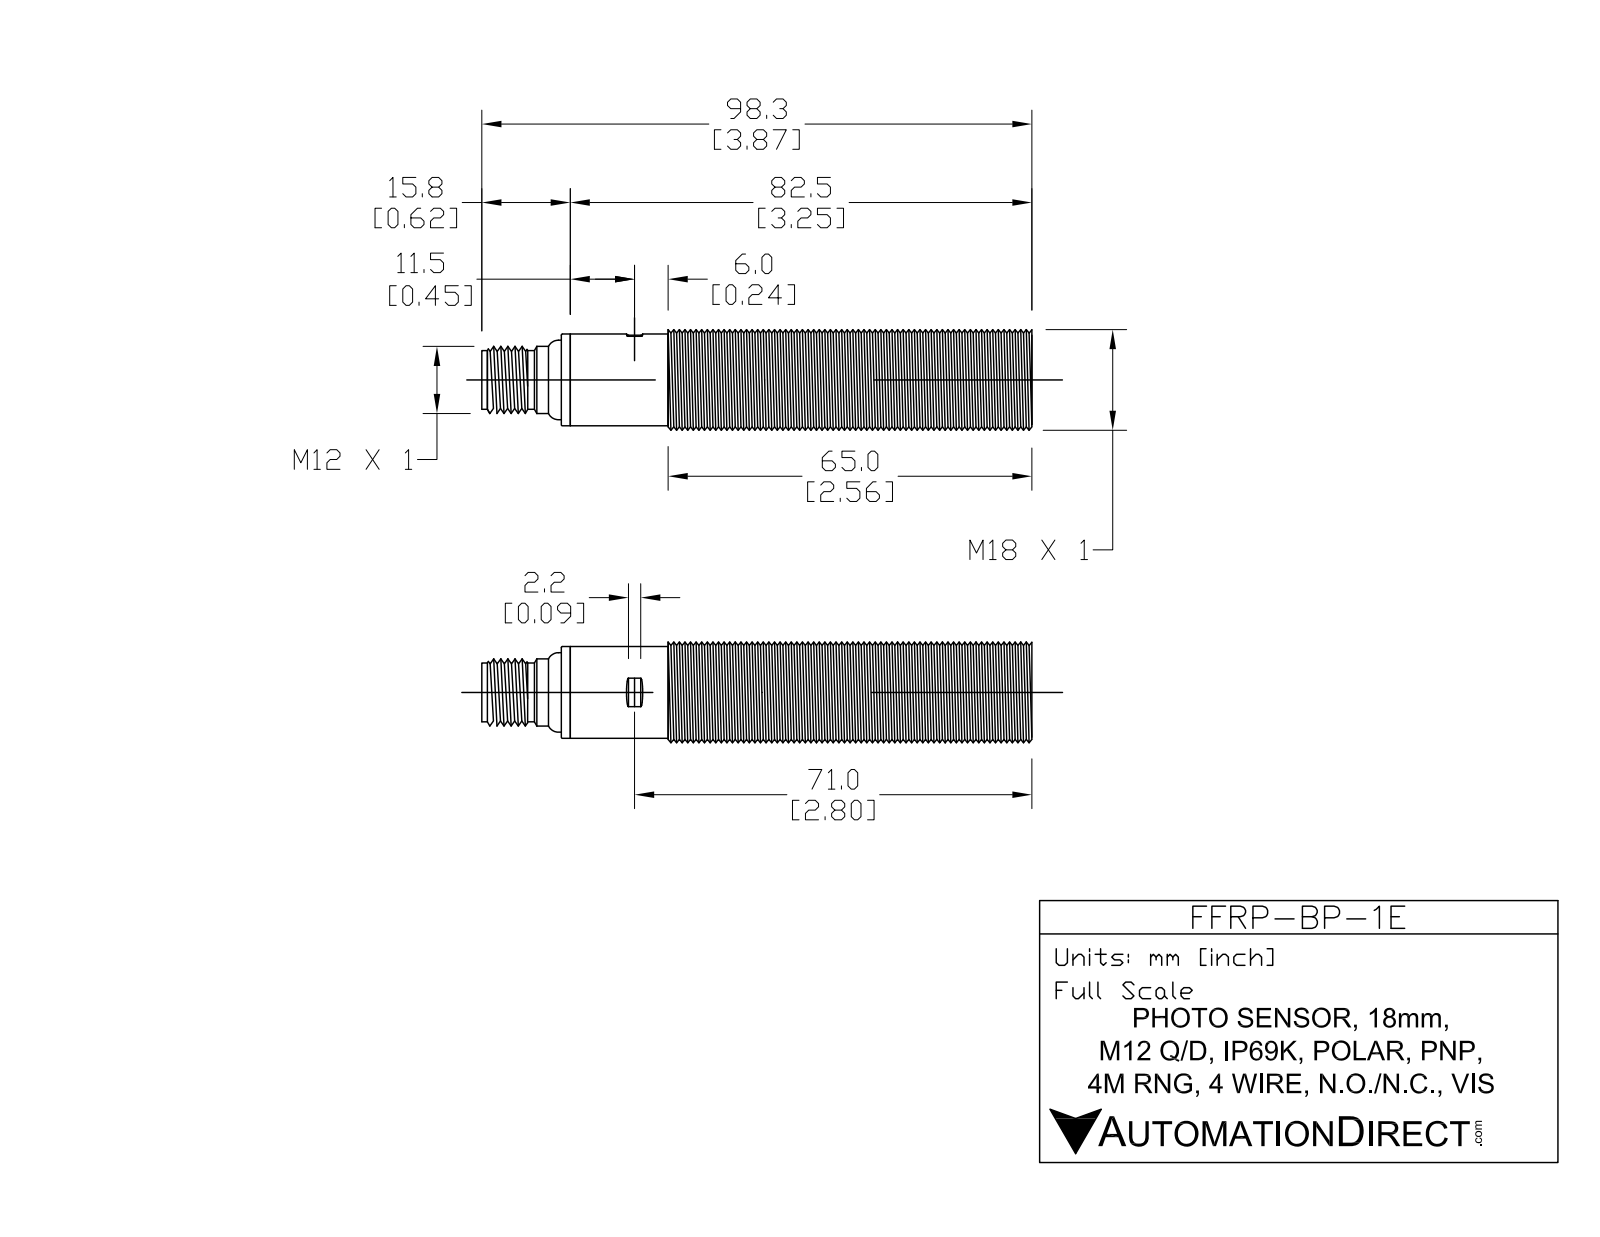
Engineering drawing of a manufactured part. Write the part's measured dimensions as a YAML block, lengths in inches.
part_name: "FFRP-BP-1E"
step_written_by: "SolidWorks 2017 (AUTOMOTIVE_DESIGN)"
units: inches
bodies: {solids: 5, faces: 118, planar: 21, cylindrical: 48, other: 49}
overall_size: [3.268, 0.709, 0.709]
volume: 1.081
surface_area: 10.47
round_holes:
  - {diameter: 0.278, count: 1}
  - {diameter: 0.327, count: 1}
  - {diameter: 0.5, count: 1}
  - {diameter: 0.583, count: 1}
  - {diameter: 0.61, count: 1}
round_bosses_or_shafts:
  - {diameter: 0.039, count: 4}
  - {diameter: 0.709, count: 1}
  - {diameter: 0.646, count: 1}
  - {diameter: 0.612, count: 1}
  - {diameter: 0.604, count: 1}
  - {diameter: 0.559, count: 1}
  - {diameter: 0.492, count: 1}
  - {diameter: 0.472, count: 1}
partial_cylinders:
  - {radius: 0.024, count: 1}
  - {radius: 0.63, count: 1}
face_to_face_distances: [2.539, 0.118, 2.657, 0.024, 0.094, 2.634, 2.717, 2.693, 2.598, 0.059]
